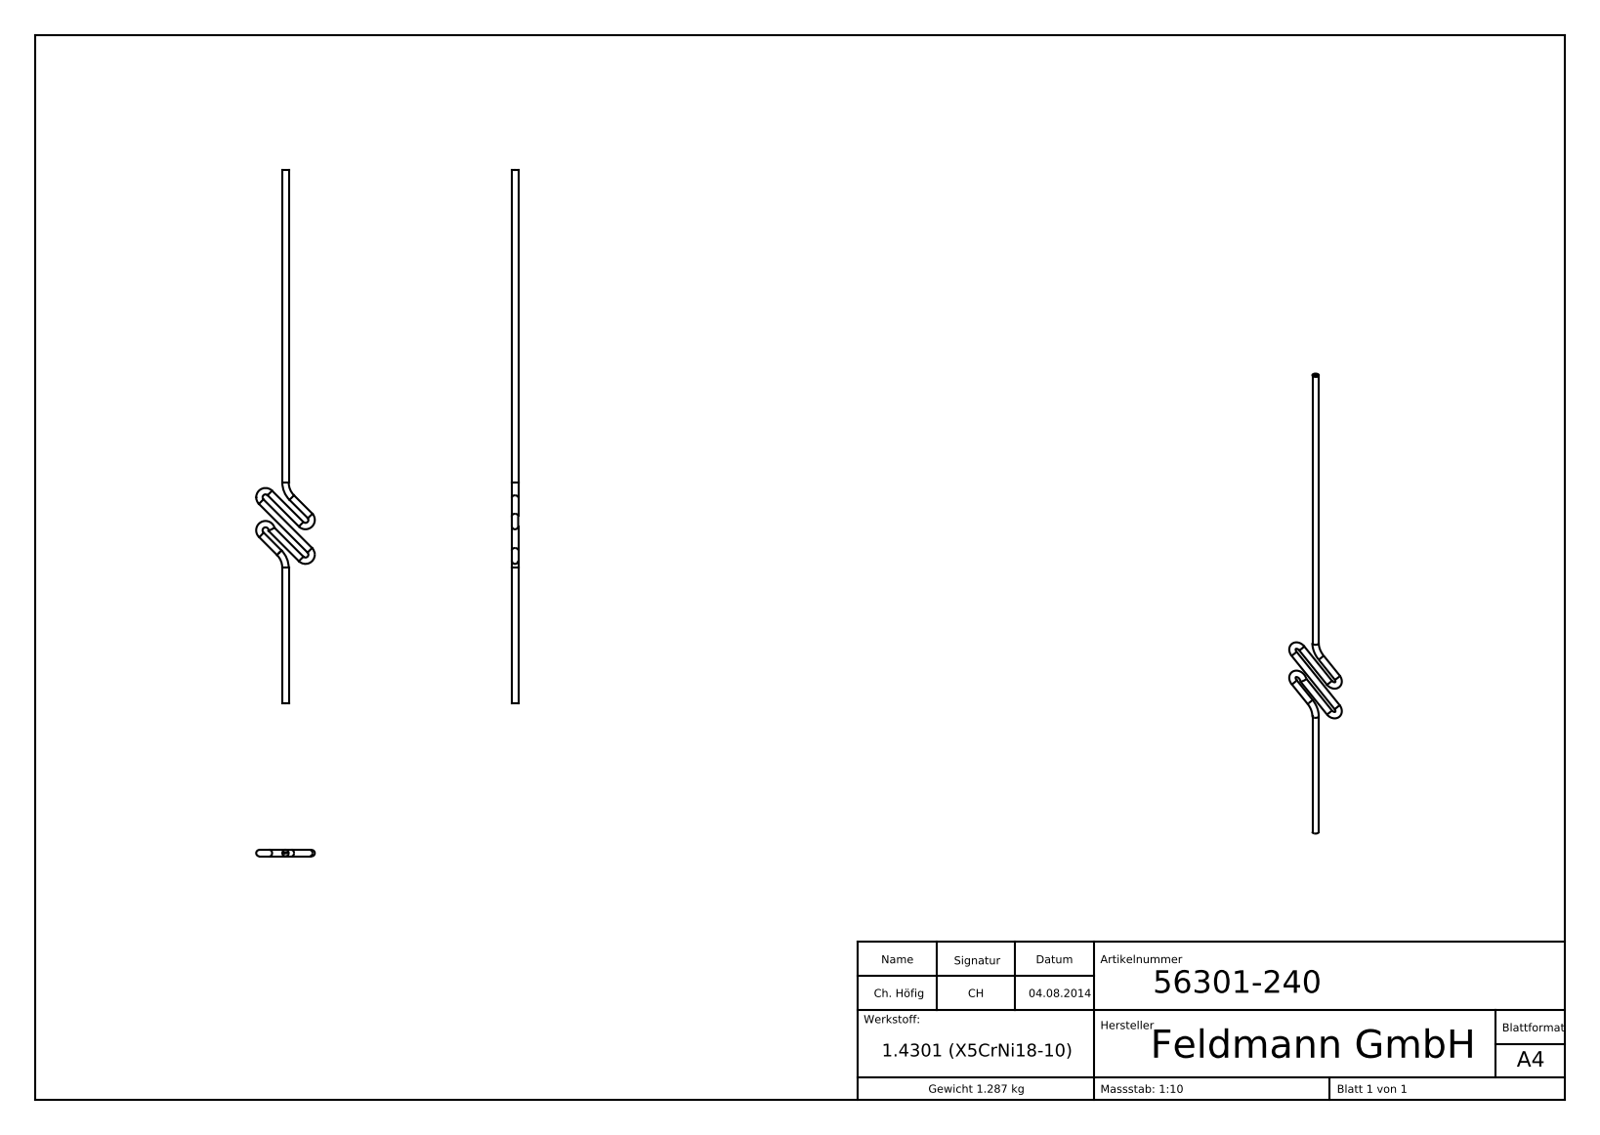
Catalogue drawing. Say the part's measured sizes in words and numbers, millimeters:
The part is named "56301-240". Its 3-D file was written by "SolidWorks 2015 (CONFIG_CONTROL_DESIGN)". It is 1 solid with 147 faces: 67 planar, 12 cylindrical and 68 other. Overall it measures 999.97 by 110 by 12 millimeters. Its volume is 162 323 cubic millimeters and its surface area 54 358 square millimeters. Round bosses or shafts: 5 of diameter 12. The main face-to-face distances are 999.97, 999.47, 0.5, 0.39, 2.97, 1.12, 4.09, 0.73, 1.26, 3.27.
